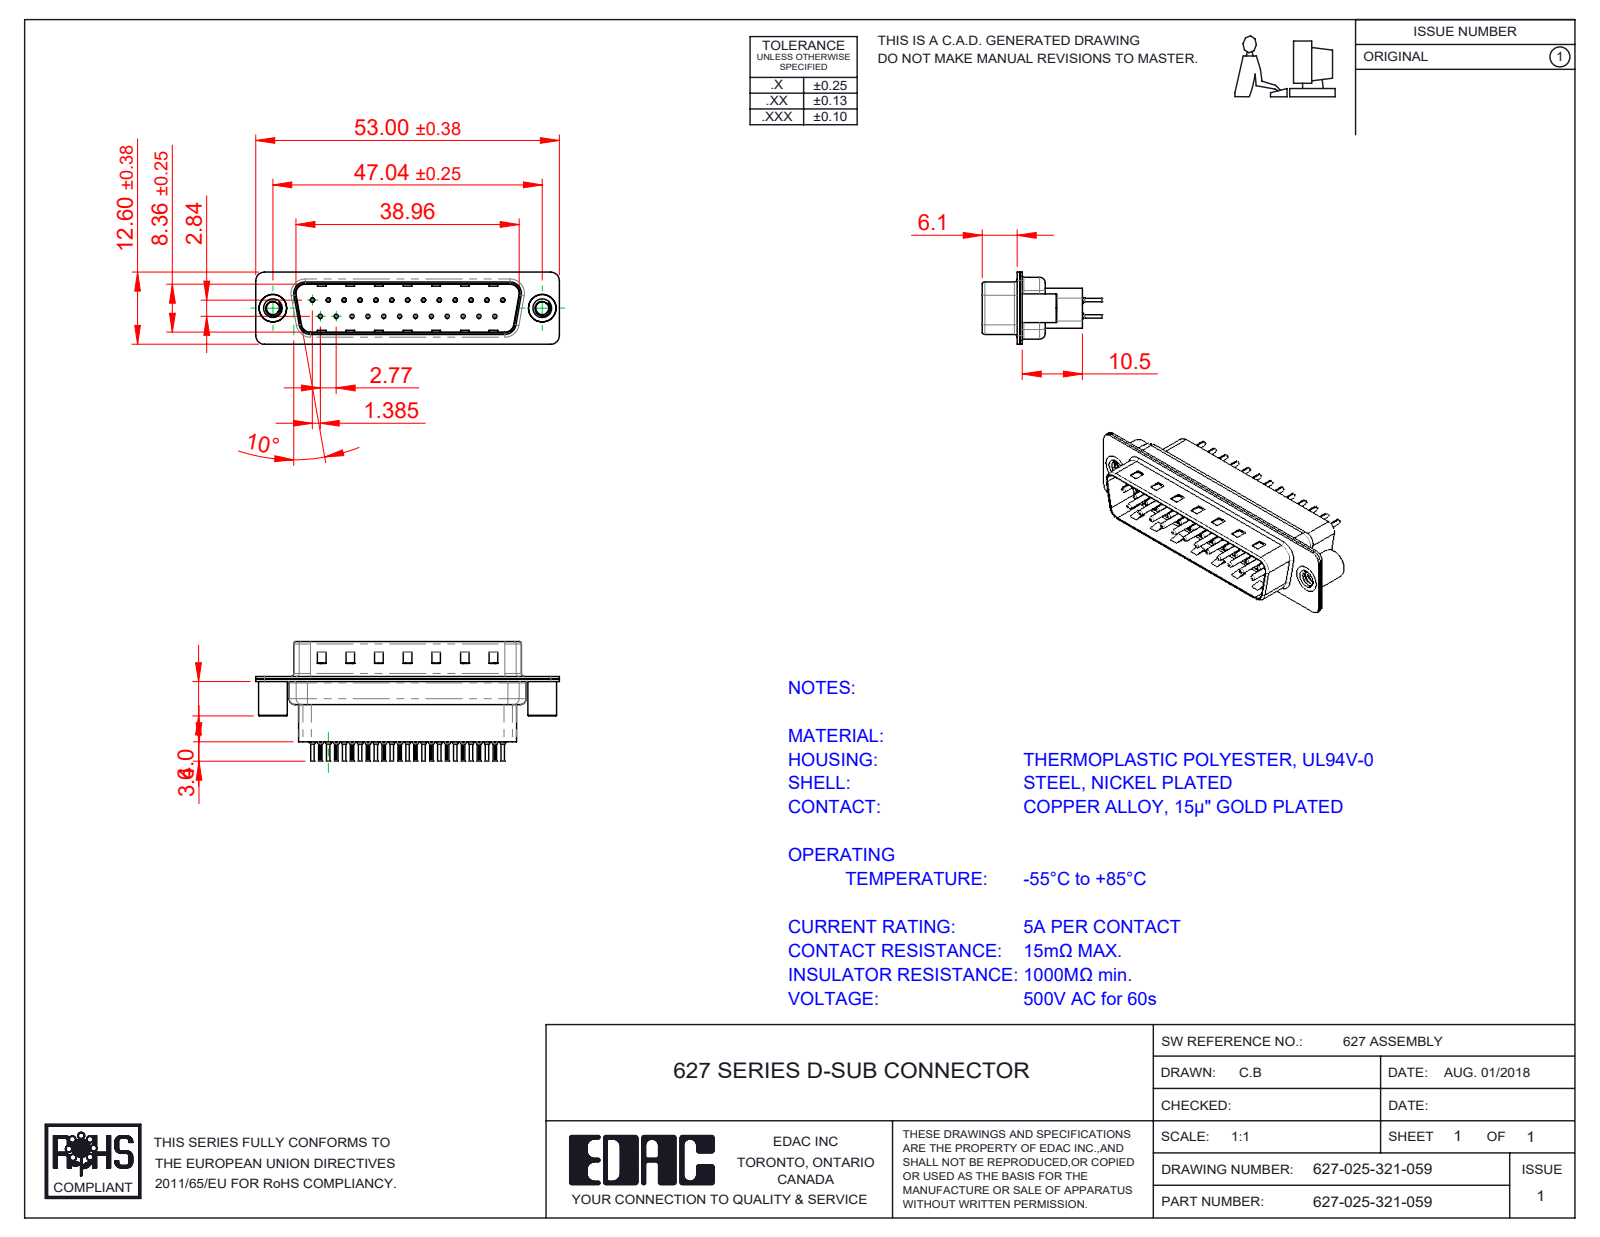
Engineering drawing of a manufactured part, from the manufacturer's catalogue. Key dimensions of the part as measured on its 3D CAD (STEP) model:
Part name (STEP PRODUCT): 627 Shell Rear_25 Contacts; 627-025-321-059; 627 4-40 Threaded Standoff BS; 627 Contact Row 1_21H (+3 more)
STEP written by: SolidWorks 2020 (CONFIG_CONTROL_DESIGN)
Units: millimetres
Bodies: 30 solids, 2848 faces (771 planar, 1082 cylindrical, 995 other)
Overall size (bounding box): 53 × 20.8 × 12.6
Volume: 3 895 mm³ · Surface area: 9 968 mm²
Round holes (diameter × count): ⌀0.2 ×25, ⌀0.35 ×25, ⌀1.1 ×25, ⌀1.6 ×25, ⌀2.26 ×2, ⌀4 ×2, ⌀4.8 ×2
Round bosses / shafts (diameter × count): ⌀2 ×25, ⌀1.5 ×25, ⌀0.75 ×25, ⌀0.6 ×25, ⌀5 ×2, ⌀4.9 ×2
Partial cylindrical surfaces — rounded edges, fillets, slot ends (radius × count): R0.1 ×50, R1.5 ×16, R2 ×12, R0.5 ×8, R1.6 ×8, R0.25 ×4, R0.6 ×4, R0.65 ×4
Main face-to-face distances: 0.4, 0.45, 0.82, 9.58, 0.68, 7.68, 1.5, 0.9, 1.08, 8.08
Hole centre spacings: 3.16, 8.31, 2.77, 5.54, 11.08, 16.62, 5.03, 5.04
